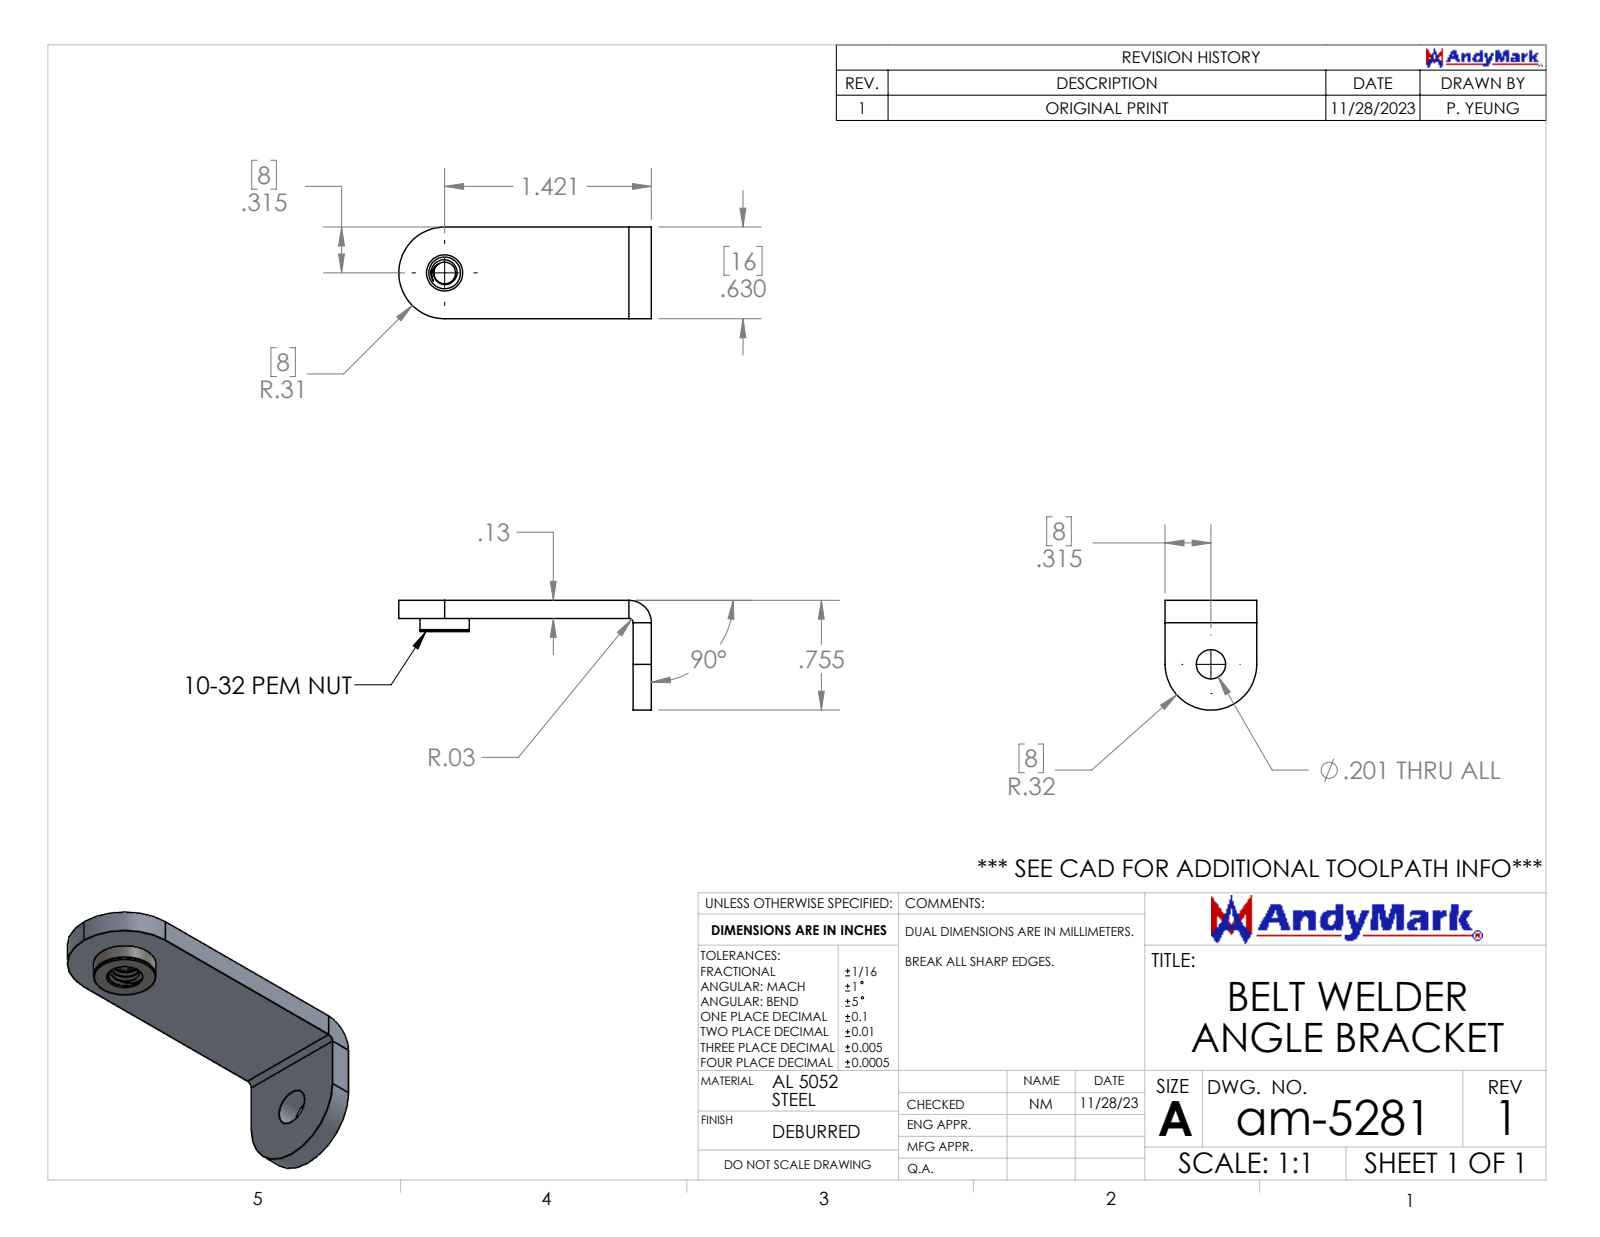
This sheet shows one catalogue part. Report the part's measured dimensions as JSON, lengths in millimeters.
{"part_name": "10-32 PEM Nut (S-032-1)_95185A185; ip-5281 Belt Welder Angle Bracket; am-5281 Belt Welder Angle Bracket", "step_written_by": "SolidWorks 2024 (AUTOMOTIVE_DESIGN)", "units": "millimeters", "bodies": {"solids": 2, "faces": 160, "planar": 63, "cylindrical": 79, "other": 18}, "overall_size": [44.1, 19.2, 16], "volume_mm3": 2790, "surface_area_mm2": 2457, "round_holes": [[4.8, 1], [5.1, 1], [6.3, 1]], "round_bosses_or_shafts": [[8.6, 1]], "partial_cylinders_radius": [[0.2, 48], [0.8, 1], [3.9, 1], [8, 1], [8, 1]], "face_to_face_distances": [3.2, 3.2, 16, 2.3, 5.5, 2.5, 2.9, 3.3, 1, 0.7]}
